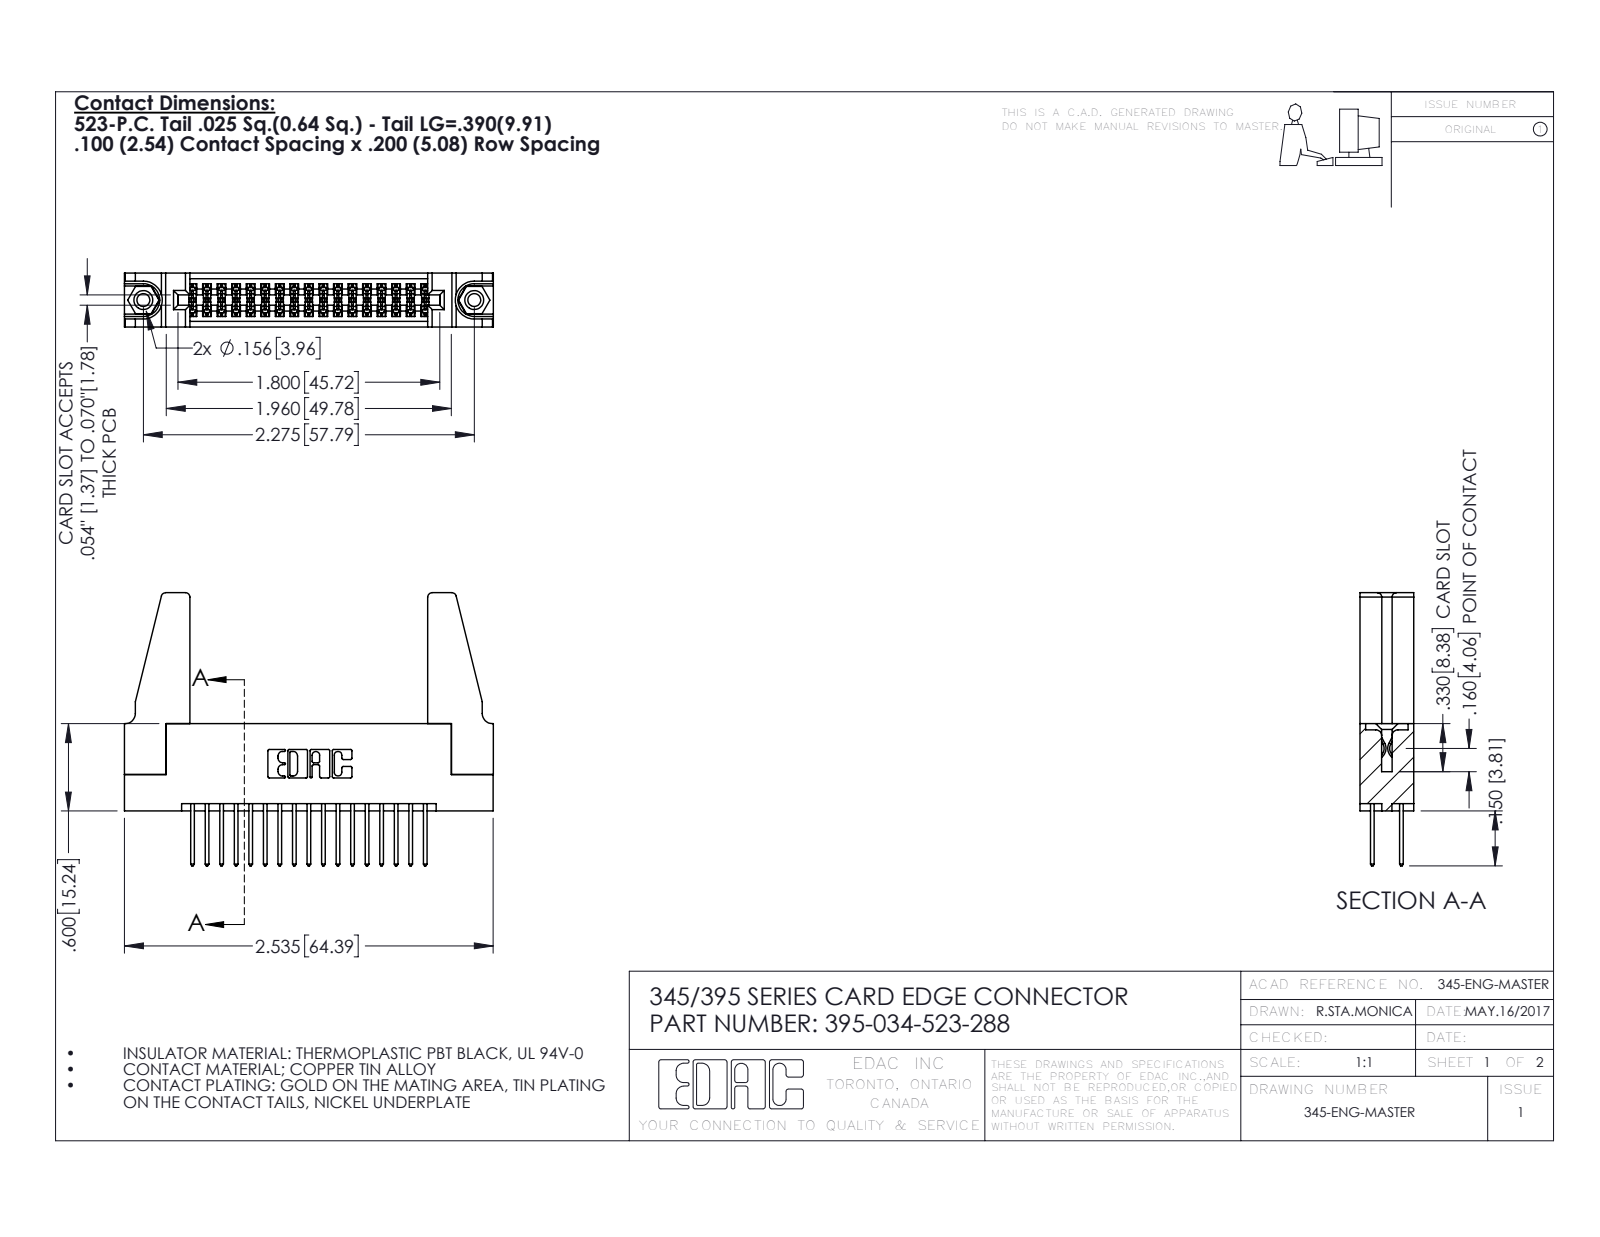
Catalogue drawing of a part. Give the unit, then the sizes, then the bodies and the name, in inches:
Units: inches
Overall size (bounding box): 2.536 × 1.877 × 0.37
Round holes (diameter × count): ⌀0.089 ×2, ⌀0.125 ×2, ⌀0.156 ×2, ⌀0.064 ×1
Round bosses / shafts (diameter × count): ⌀0.155 ×2
Partial cylindrical surfaces — rounded edges, fillets, slot ends (radius × count): R0.006 ×51, R0.01 ×34, R0.01 ×22, R0.03 ×8, R0.007 ×6, R0.031 ×6, R0.026 ×3, R0.014 ×2
Main face-to-face distances: 0.072, 0.298, 0.37, 0.2, 0.098, 0.272, 0.025, 0.225, 0.175, 0.15
Hole centre spacings: 0.27, 2.041, 2.275
Volume: 0.57 in³ · Surface area: 18.54 in²
Bodies: 39 solids, 1950 faces (1274 planar, 660 cylindrical, 16 other)
Part name (STEP PRODUCT): 345-250-001_345-250-001-102; 345-292-001_345-293-123; 345-220-078_345-220-088; 345 Part_Flush Mounting Lugs - 0.156 Dia-TH (+1 more)
STEP written by: SolidWorks 2016 (CONFIG_CONTROL_DESIGN)
